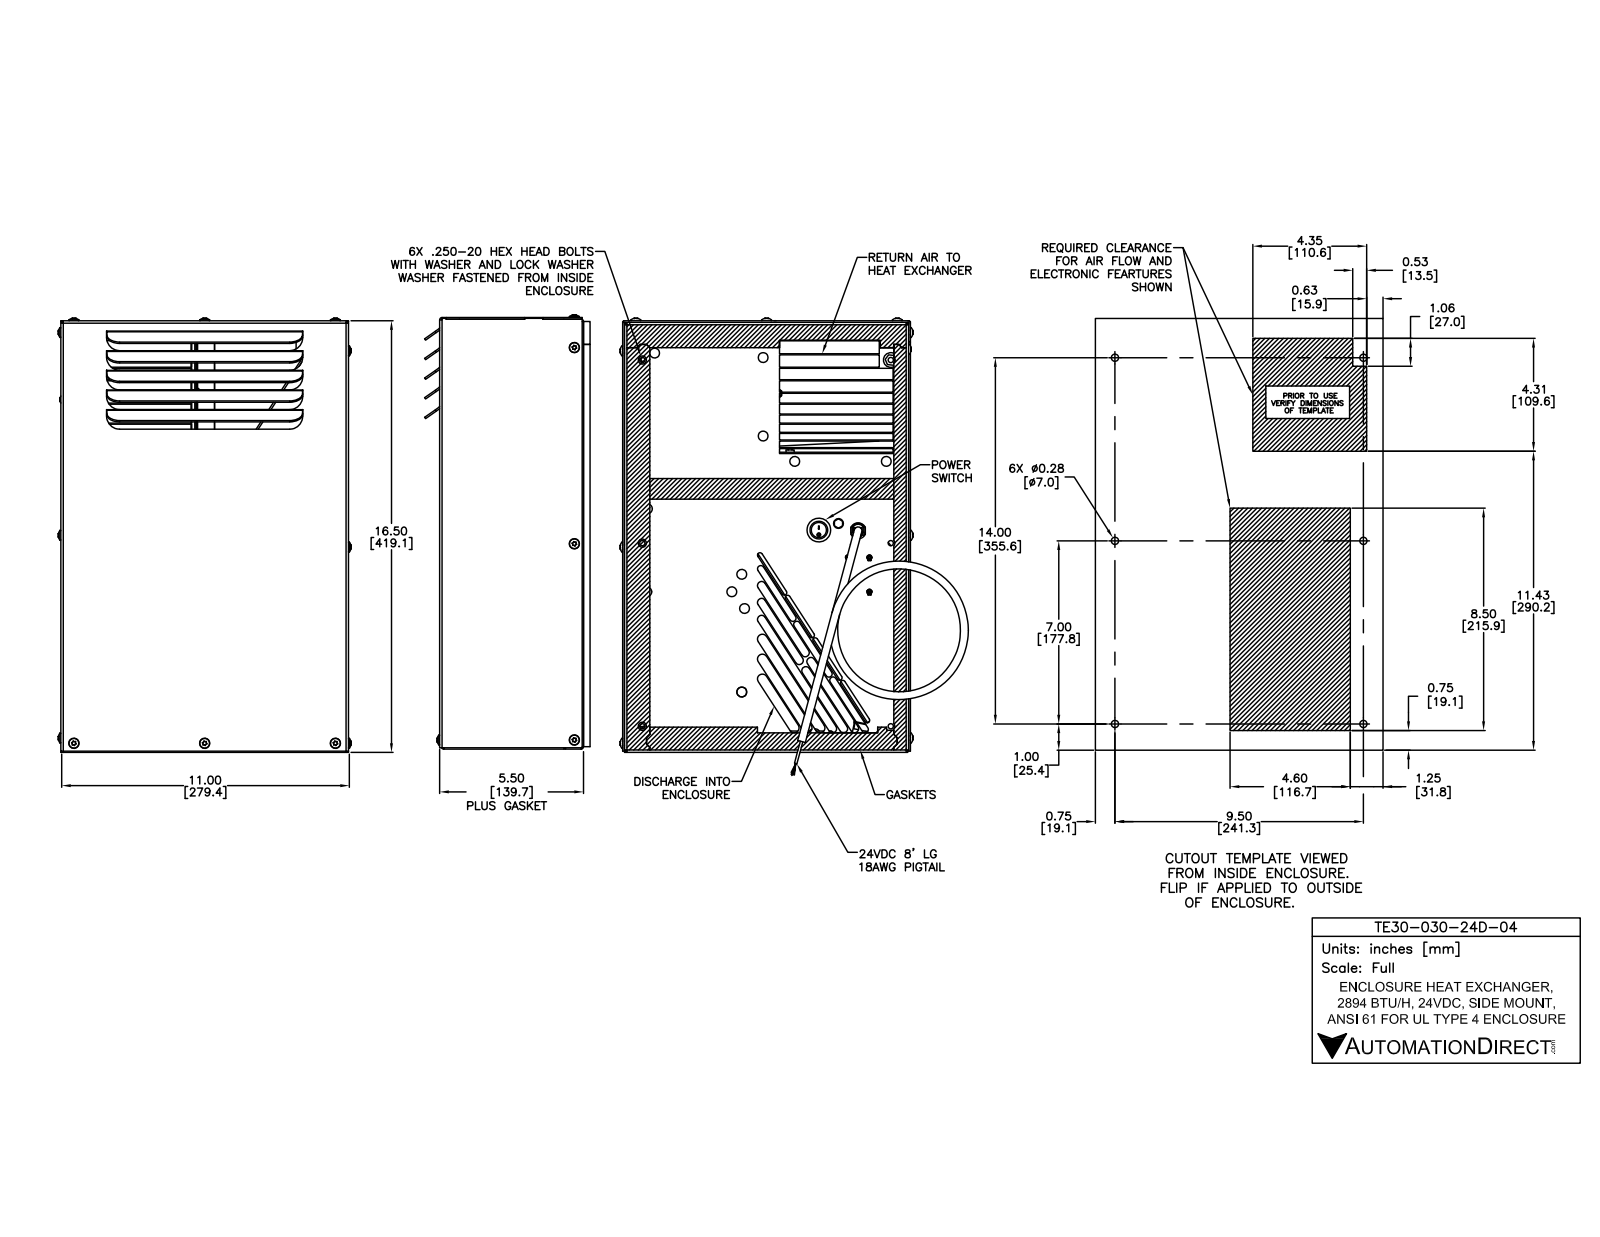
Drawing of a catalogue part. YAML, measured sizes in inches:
part_name: "TE30-030-24D-04"
step_written_by: "SolidWorks 2017 (AUTOMOTIVE_DESIGN)"
units: inches
bodies: {solids: 122, faces: 3166, planar: 1807, cylindrical: 975, other: 384}
overall_size: [16.594, 11.188, 6.463]
volume: 170.6
surface_area: 3102
round_holes:
  - {diameter: 0.188, count: 23}
  - {diameter: 0.193, count: 23}
  - {diameter: 0.219, count: 19}
  - {diameter: 0.5, count: 16}
  - {diameter: 0.203, count: 9}
  - {diameter: 0.156, count: 8}
  - {diameter: 0.109, count: 7}
  - {diameter: 0.195, count: 6}
  - {diameter: 0.2, count: 6}
  - {diameter: 0.201, count: 6}
  - {diameter: 0.25, count: 6}
  - {diameter: 0.272, count: 6}
round_bosses_or_shafts:
  - {diameter: 0.27, count: 23}
  - {diameter: 0.19, count: 15}
  - {diameter: 0.564, count: 6}
  - {diameter: 0.44, count: 6}
  - {diameter: 0.344, count: 6}
  - {diameter: 0.326, count: 6}
  - {diameter: 0.325, count: 6}
  - {diameter: 0.311, count: 6}
partial_cylinders:
  - {radius: 0.01, count: 84}
  - {radius: 0.015, count: 84}
  - {radius: 0.031, count: 59}
  - {radius: 0.093, count: 46}
  - {radius: 0.101, count: 18}
  - {radius: 0.06, count: 17}
  - {radius: 0.094, count: 13}
  - {radius: 0.125, count: 12}
face_to_face_distances: [0.062, 0.062, 10.871, 5.5, 5.376, 5.438, 5.438, 10.933, 10.809, 1.083]
hole_center_spacings: [1.25, 2.5, 3.75, 1.296, 1.205, 2.546, 0.06, 3.25]
